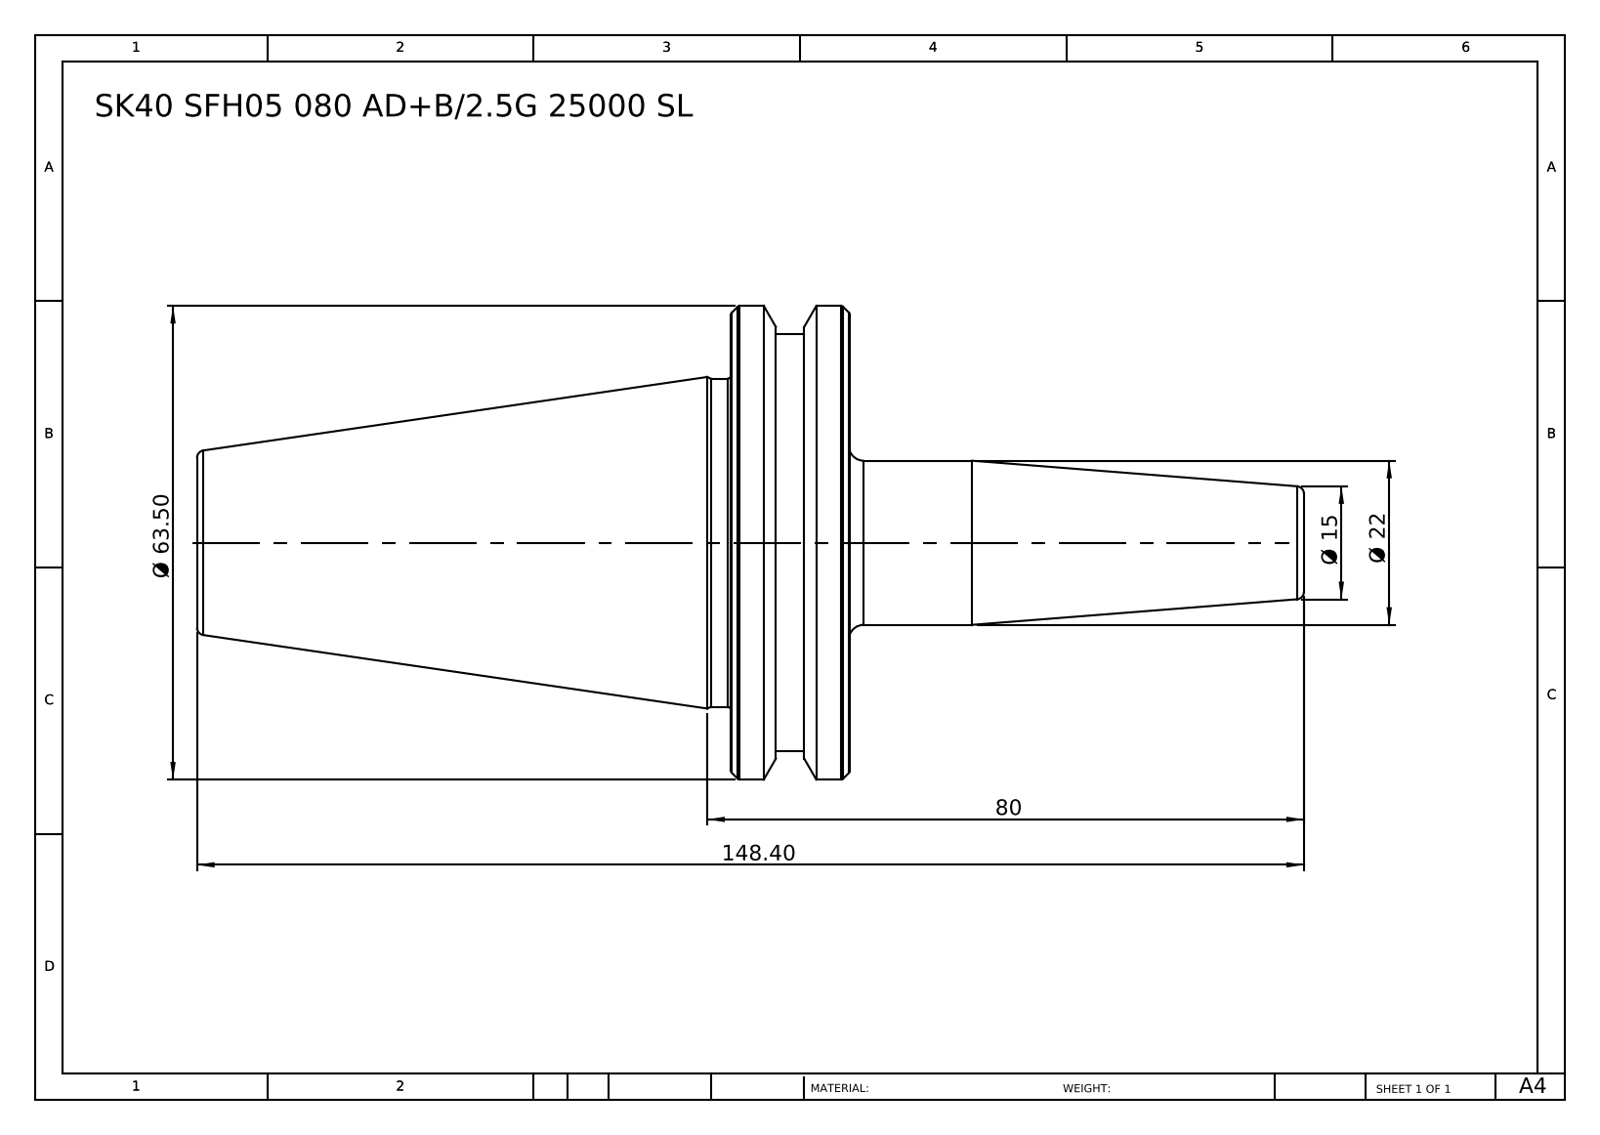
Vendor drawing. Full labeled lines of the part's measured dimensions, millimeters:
Part name (STEP PRODUCT): SK40 SFH05 80 AD+B-2.5G 25000 SL
STEP written by: SolidWorks 2014 (CONFIG_CONTROL_DESIGN)
Units: millimetres
Bodies: 1 solid, 46 faces (6 planar, 10 cylindrical, 30 other)
Overall size (bounding box): 148.4 × 63.5 × 63.5
Volume: 135 478 mm³ · Surface area: 20 383 mm²
Round bosses / shafts (diameter × count): ⌀63.5 ×1, ⌀56 ×1, ⌀44 ×1, ⌀22 ×1
Main face-to-face distances: 15.9, 87.5, 71.6, 6.1, 9.8, 81.4, 9.9, 3.8, 6, 77.6
